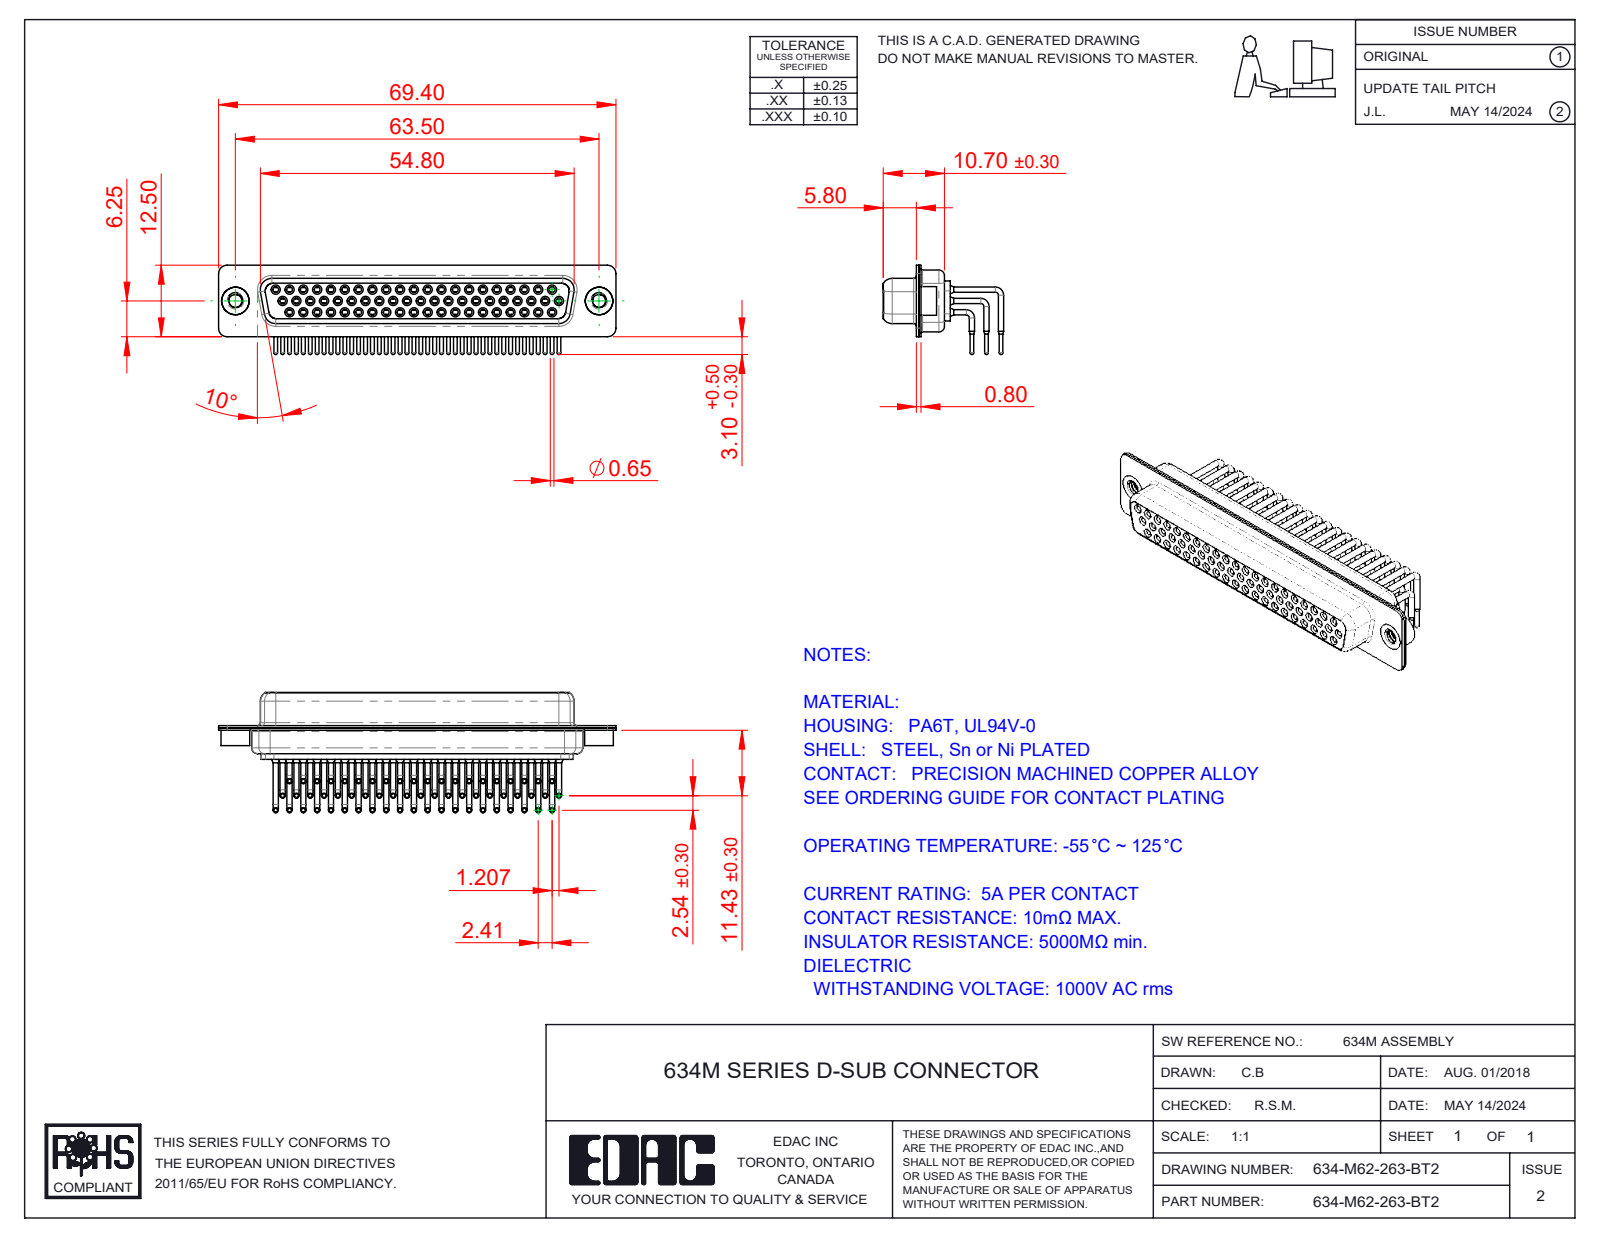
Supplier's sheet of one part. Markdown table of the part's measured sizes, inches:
| quantity | value |
| --- | --- |
| part name | 634M Contact Row 2; 634M Contact Row 3; 634M Housing_62 Contacts; 634M Contact Row 1 (+4 more) |
| STEP written by | SolidWorks 2016 (CONFIG_CONTROL_DESIGN) |
| units | inches |
| bodies | 67 solids, 3565 faces (997 planar, 1563 cylindrical, 1005 other) |
| overall size | 2.732 × 0.828 × 0.614 |
| volume | 0.33 in³ |
| surface area | 27.7 in² |
| round holes (diameter × count) | 0.039 × 62, 0.043 × 62, 0.067 × 62, 0.071 × 62, 0.079 × 62, 0.089 × 2, 0.157 × 2, 0.189 × 2 |
| round bosses / shafts (diameter × count) | 0.035 × 124, 0.063 × 62, 0.059 × 62, 0.026 × 62, 0.079 × 56, 0.197 × 2, 0.193 × 2 |
| partial cylindrical surfaces (radius × count) | 0.059 × 16, 0.079 × 12, 0.053 × 8, 0.063 × 8, 0.01 × 4, 0.02 × 4, 0.024 × 4, 0.026 × 4 |
| main face-to-face distances | 0.016, 0.057, 0.352, 0.075, 0.335, 0.091, 0.244, 0.018, 0.278, 0.033 |
| hole center spacings | 0.285, 0.091, 0.095, 0.38, 0.163, 0.19, 0.665, 0.57 |
